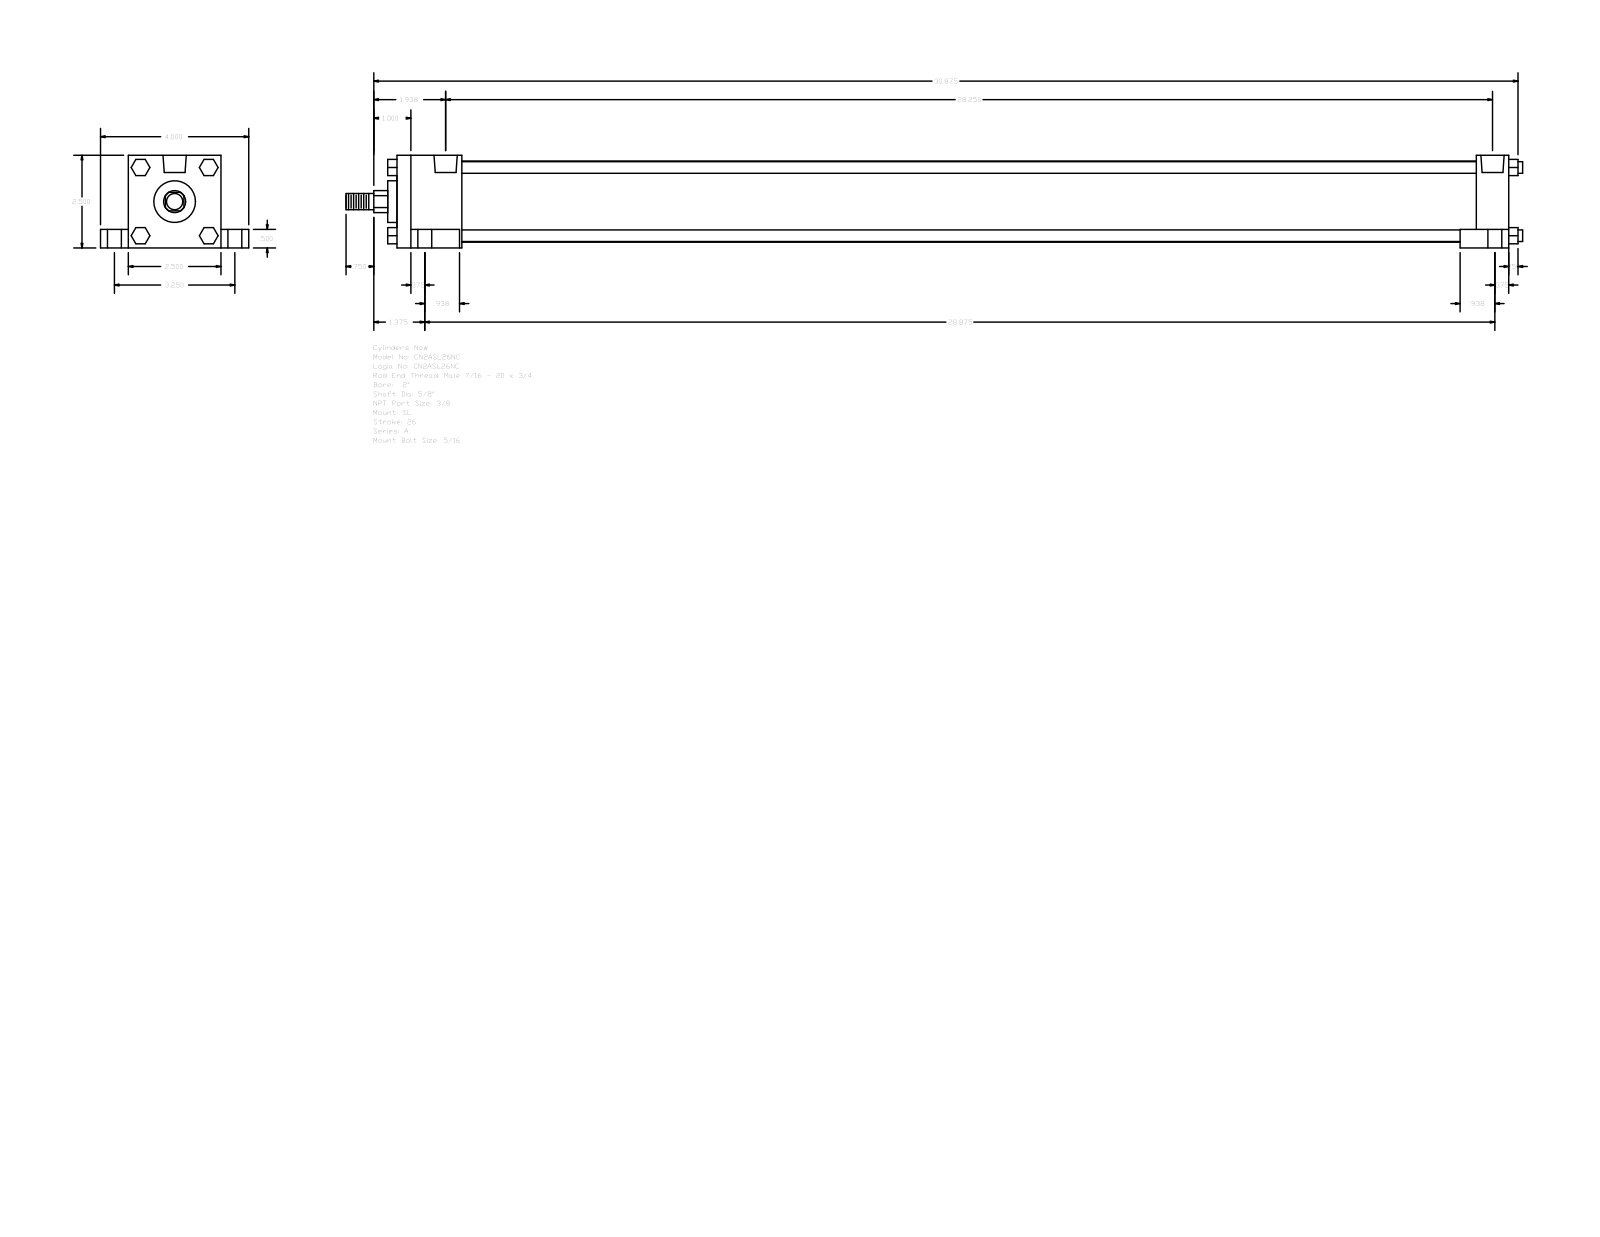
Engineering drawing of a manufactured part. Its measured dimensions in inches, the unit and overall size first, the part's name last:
Units: inches
Overall size (bounding box): 31.75 × 4 × 2.5
Round holes (diameter × count): ⌀0.219 ×4, ⌀0.375 ×4, ⌀0.625 ×4, ⌀0.627 ×2
Round bosses / shafts (diameter × count): ⌀0.313 ×4, ⌀2.19 ×1, ⌀1.125 ×1, ⌀0.625 ×1, ⌀0.437 ×1
Partial cylindrical surfaces — rounded edges, fillets, slot ends (radius × count): R0.297 ×1
Main face-to-face distances: 2.5, 30, 2, 0.5, 0.75, 3.25, 1.75, 28.25, 29.125, 27.375
Hole centre spacings: 1.626, 1.639, 1.719, 1.777, 3.25, 27.937, 28.203, 28.359
Bodies: 0 solids, 148 faces (112 planar, 36 cylindrical, 0 other)
Part name (STEP PRODUCT): A_SL__0200_0.625
STEP written by: GSSL Pune (CONFIG_CONTROL_DESIGN)
